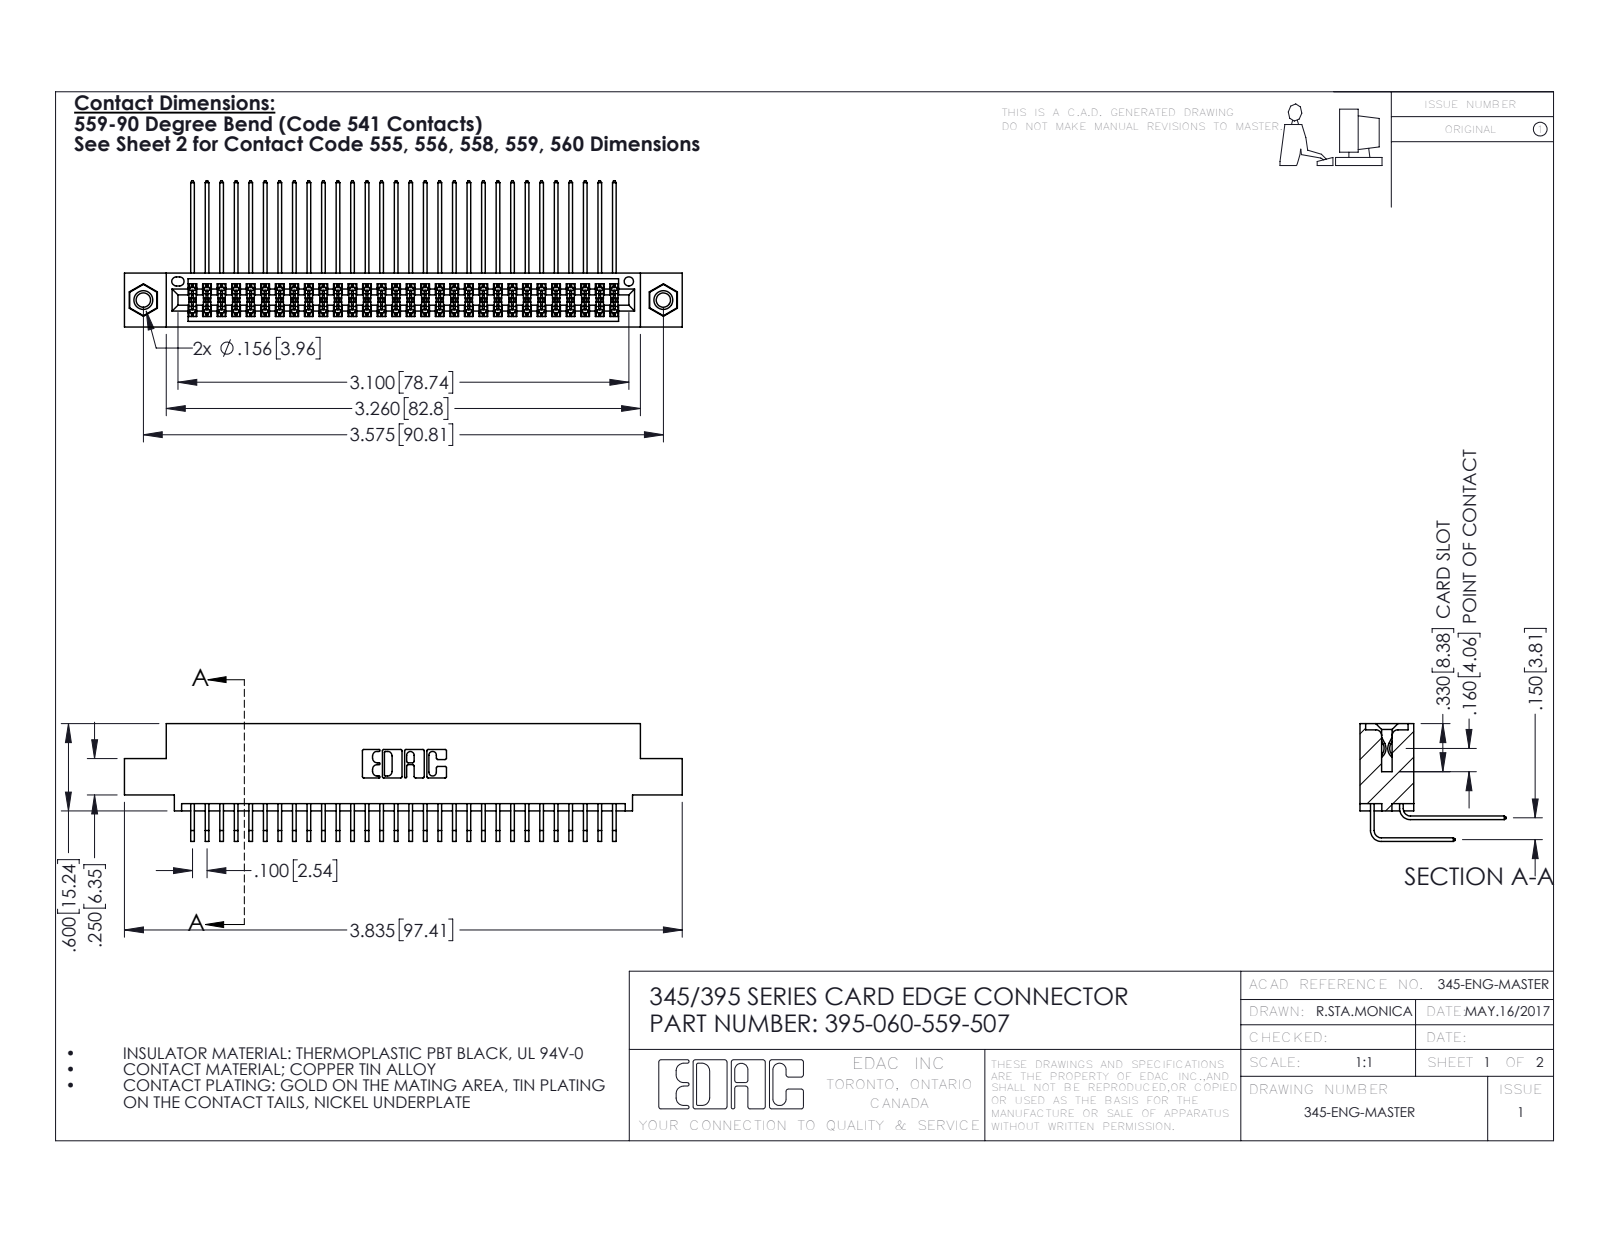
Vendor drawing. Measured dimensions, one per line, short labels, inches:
name: 345-292-001_559 Tail - 2; 345-292-001_558 559 Tail - 1; 345-250-001_345-250-005-103; 395-060-559-507 (+1 more)
written by: SolidWorks 2016 (CONFIG_CONTROL_DESIGN)
unit: in
bodies: 63 solids, 3310 faces (2216 planar, 1078 cylindrical, 16 other)
size: 3.835 × 1.005 × 0.809
volume: 0.586 in³; area: 24.37 in²
holes: 2× ⌀0.098, 2× ⌀0.125, 2× ⌀0.156, 1× ⌀0.064
bosses: 2× ⌀0.155
rounds: 90× R0.006, 22× R0.01, 6× R0.007, 6× R0.031, 3× R0.026, 2× R0.014, 2× R0.019, 2× R0.022
face distances: 0.072, 0.298, 0.2, 0.37, 0.098, 0.272, 0.025, 0.225, 0.15, 0.175
hole spacings: 0.27, 3.34, 3.575
